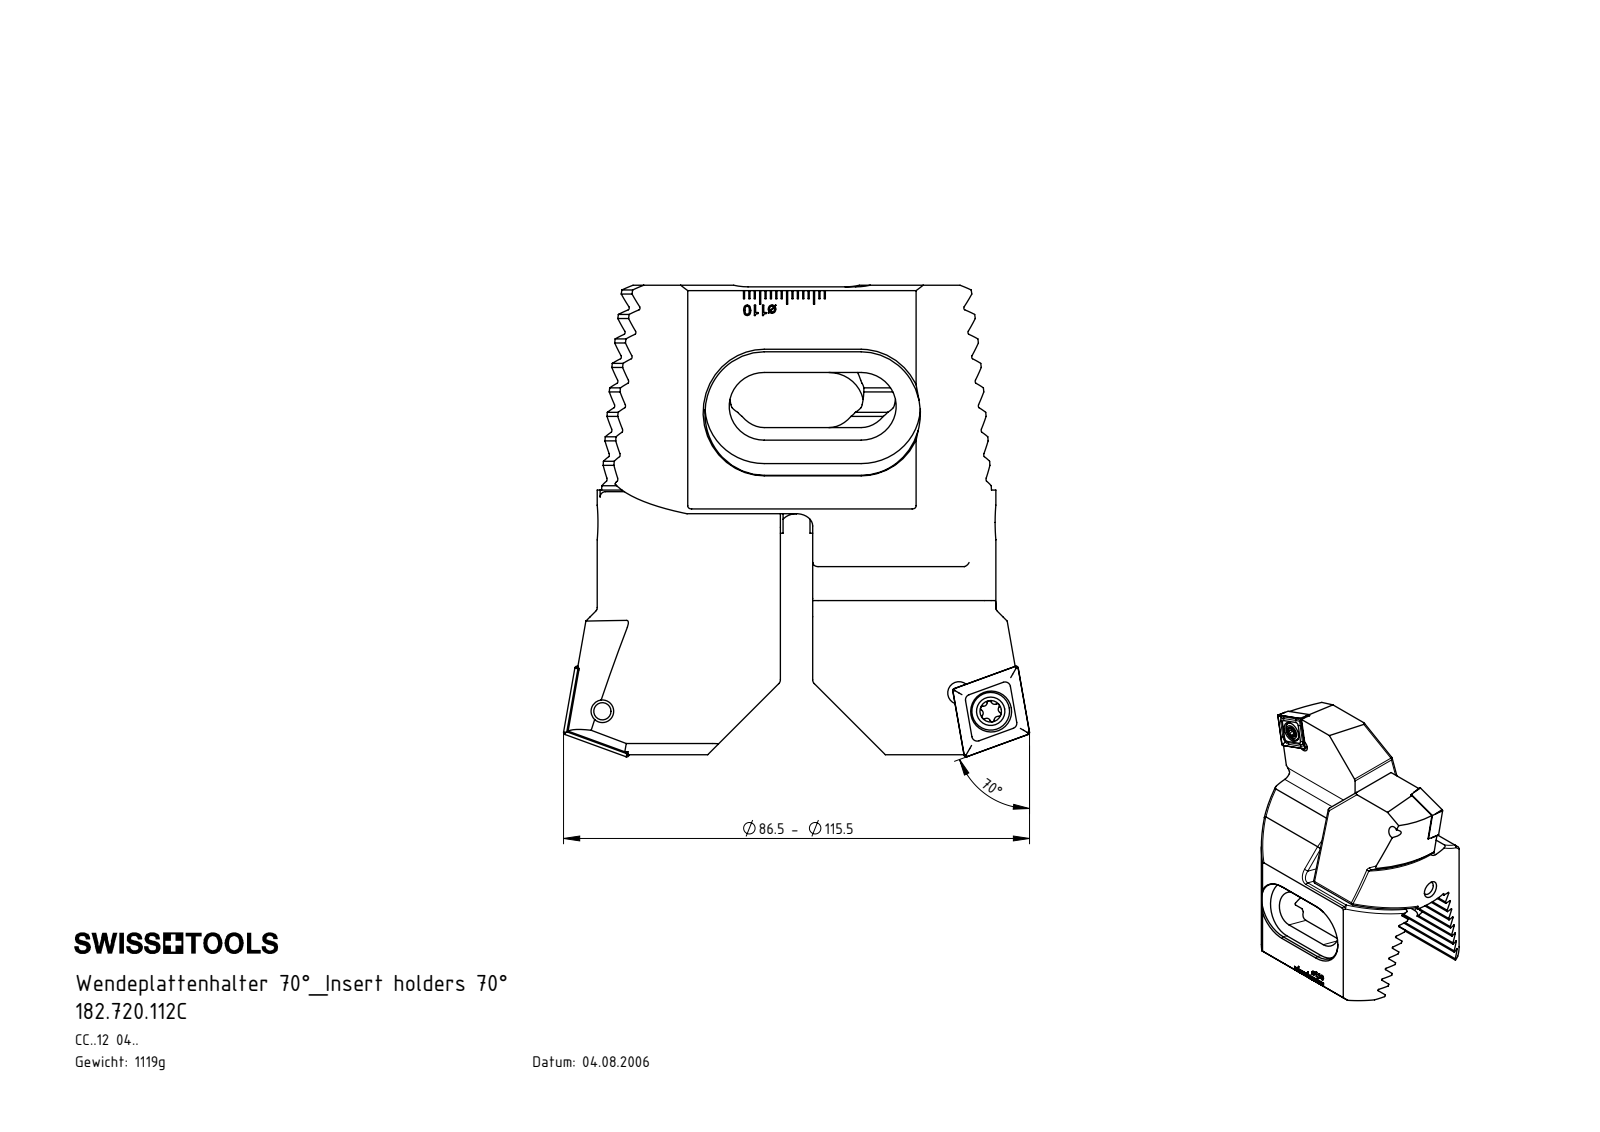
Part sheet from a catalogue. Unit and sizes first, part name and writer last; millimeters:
Units: millimetres
Overall size (bounding box): 87.5 × 86.5 × 58.2
Round holes (diameter × count): ⌀4.2 ×4, ⌀2 ×2, ⌀5.5 ×2, ⌀7.6 ×2, ⌀5 ×1
Round bosses / shafts (diameter × count): ⌀7 ×2, ⌀5 ×2, ⌀6 ×1, ⌀4 ×1
Partial cylindrical surfaces — rounded edges, fillets, slot ends (radius × count): R0.34 ×16, R1 ×16, R0.39 ×12, R0.69 ×8, R3 ×6, R0.69 ×4, R6.5 ×4, R11 ×4
Main face-to-face distances: 4.07, 8.14, 28.8, 29.4, 20.36, 12.21, 58.2, 16.29, 20.34, 24.43
Hole centre spacings: 6.79, 6.88, 20, 66.29, 66.37, 72.16, 38.64, 60.32
Volume: 143 895 mm³ · Surface area: 37 756 mm²
Bodies: 8 solids, 730 faces (398 planar, 138 cylindrical, 194 other)
Part name (STEP PRODUCT): WCC-ER2.001.010_A; Z72-xxx.001.050_C_CC 12_70ø; CCMT120404; 182.720.112C (+1 more)
STEP written by: SolidWorks 2017 (CONFIG_CONTROL_DESIGN)
